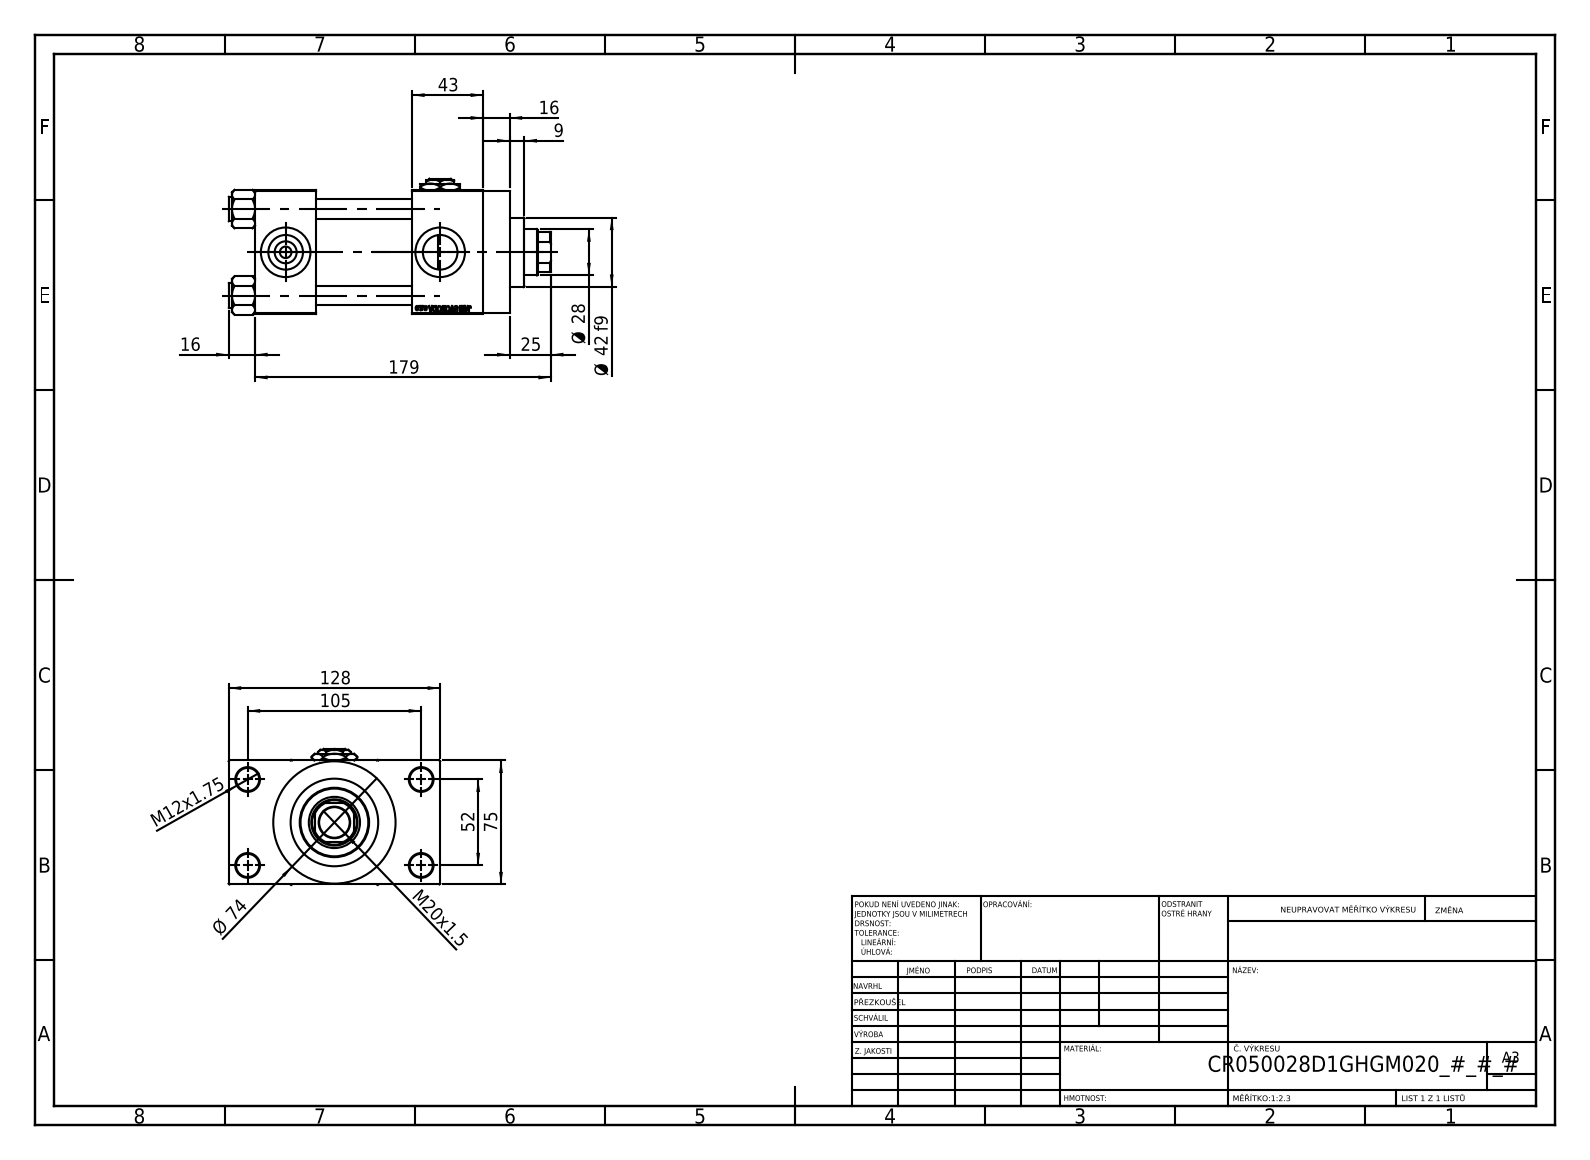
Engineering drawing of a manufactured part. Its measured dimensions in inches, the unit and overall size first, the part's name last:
Units: inches
Overall size (bounding box): 7.677 × 5.039 × 3.239
Round holes (diameter × count): ⌀0.472 ×4, ⌀0.551 ×4, ⌀0.825 ×3, ⌀1.181 ×3, ⌀0.276 ×2, ⌀0.728 ×1, ⌀1.102 ×1, ⌀1.22 ×1, ⌀1.614 ×1, ⌀1.969 ×1, ⌀2.087 ×1
Round bosses / shafts (diameter × count): ⌀0.591 ×4, ⌀2.913 ×1, ⌀2.205 ×1, ⌀1.654 ×1
Partial cylindrical surfaces — rounded edges, fillets, slot ends (radius × count): R0.531 ×1
Main face-to-face distances: 2.953, 2.283, 1.457, 3.74, 1.043, 5.433, 3.976, 1.693, 3.996, 0.63
Hole centre spacings: 1.037, 1.456, 2.059, 2.3, 2.307, 3.096, 3.715, 2.047
Volume: 49.06 in³ · Surface area: 267 in²
Bodies: 12 solids, 1151 faces (521 planar, 92 cylindrical, 538 other)
Part name (STEP PRODUCT): NUT_M5_D; V215CR_VCP_D; V215CR_D_TYCINKA; V215CR_D_Body (+2 more)
STEP written by: SolidWorks 2019 (CONFIG_CONTROL_DESIGN)
